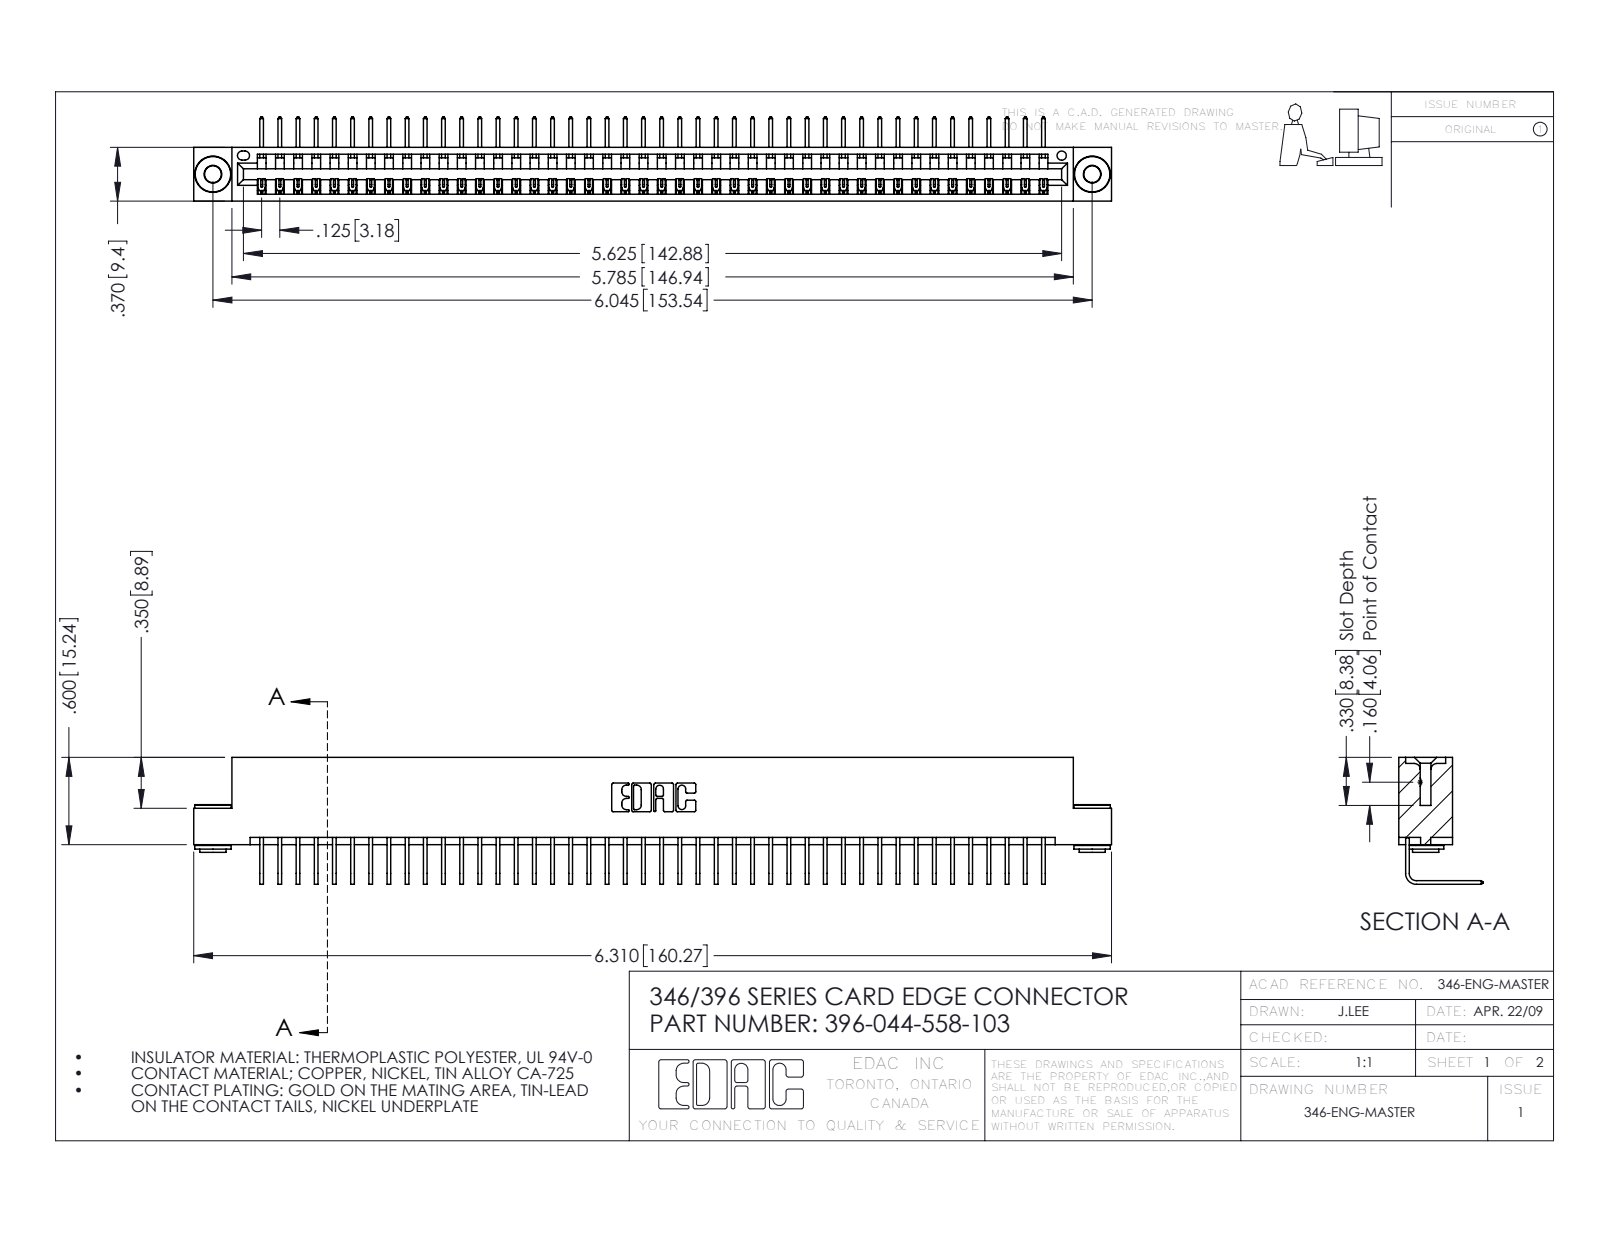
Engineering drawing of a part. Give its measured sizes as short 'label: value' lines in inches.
name: 346 Part_Flush Mounting Lugs - 0.156 Dia-TH; 396-044-558-103; 345-250-002_345-250-002-102; 345-292-001_558 Tail - 2
written by: SolidWorks 2016 (CONFIG_CONTROL_DESIGN)
unit: in
bodies: 47 solids, 2800 faces (1934 planar, 858 cylindrical, 8 other)
size: 6.31 × 0.873 × 0.58
volume: 0.947 in³; area: 31.8 in²
holes: 2× ⌀0.116, 2× ⌀0.156, 1× ⌀0.064
bosses: 2× ⌀0.25, 2× ⌀0.18, 2× ⌀0.136
rounds: 88× R0.006, 22× R0.01, 6× R0.007, 6× R0.031, 3× R0.026, 2× R0.031, 2× R0.04, 1× R0.014
face distances: 0.322, 0.048, 0.37, 0.25, 0.025, 0.298, 0.072, 0.148, 0.222, 0.1
hole spacings: 0.246, 5.836, 6.045
